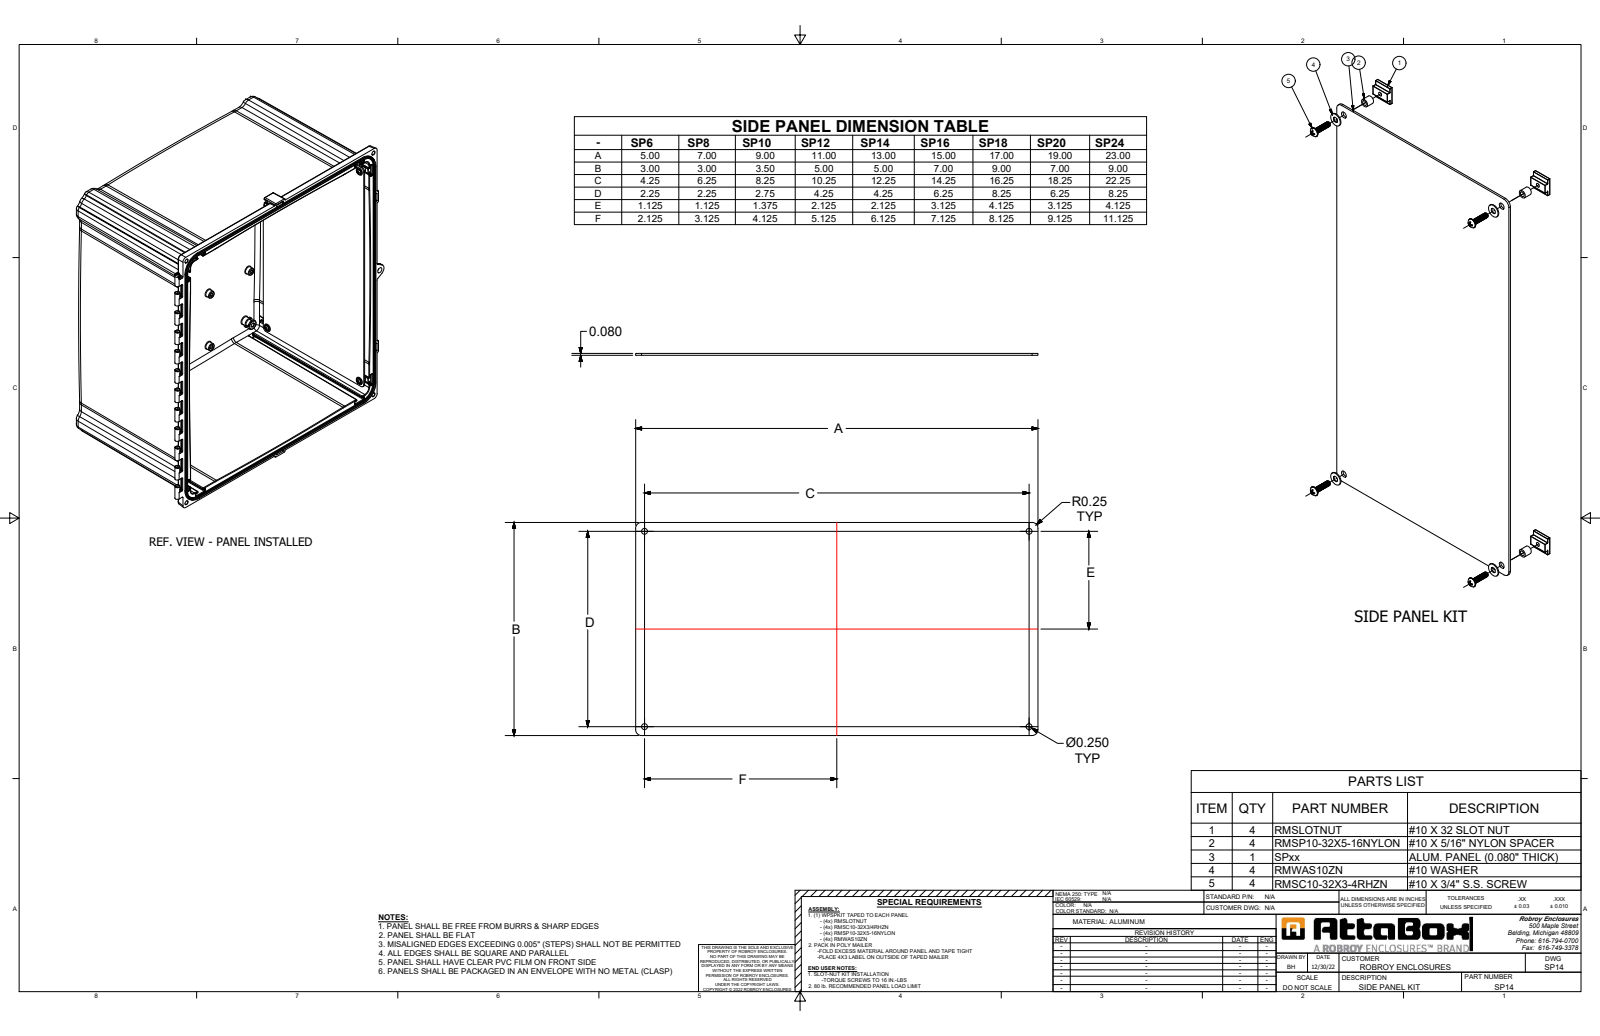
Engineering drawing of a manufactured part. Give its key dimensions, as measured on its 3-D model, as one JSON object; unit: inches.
{"part_name": "SP14_Default", "step_written_by": "SolidWorks 2023 (CONFIG_CONTROL_DESIGN)", "units": "inches", "bodies": {"solids": 1, "faces": 14, "planar": 6, "cylindrical": 8, "other": 0}, "overall_size": [13, 5, 0.08], "volume_in3": 5.18, "surface_area_in2": 132.6, "round_holes": [[0.25, 4]], "partial_cylinders_radius": [[0.25, 4]], "face_to_face_distances": [0.08, 5, 13], "hole_center_spacings": [4.25, 12.25, 12.966]}
